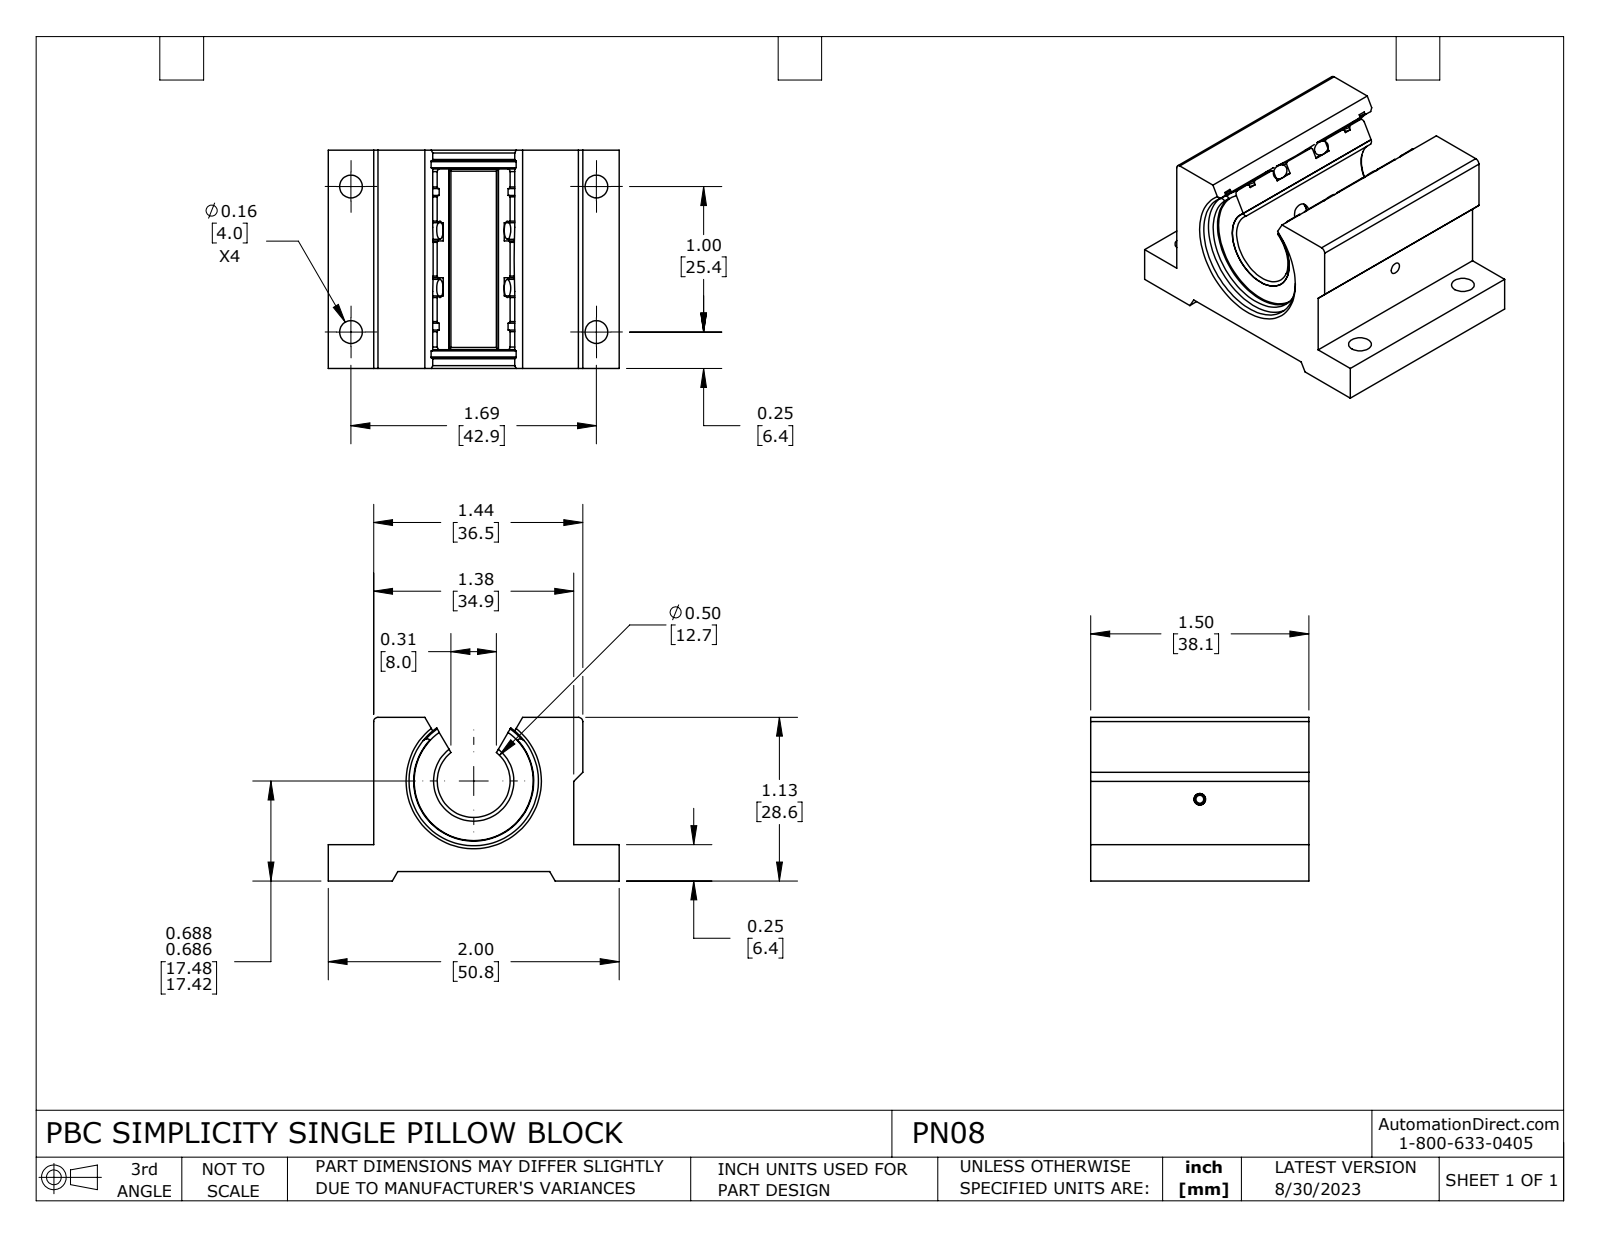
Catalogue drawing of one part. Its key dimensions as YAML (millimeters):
part_name: "PN08"
step_written_by: "SolidWorks 2021 (CONFIG_CONTROL_DESIGN)"
units: millimeters
bodies: {solids: 8, faces: 202, planar: 49, cylindrical: 94, other: 59}
overall_size: [50.8, 38.1, 28.6]
volume: 31120
surface_area: 17050
round_holes:
  - {diameter: 4, count: 4}
  - {diameter: 1.4, count: 1}
  - {diameter: 2, count: 1}
  - {diameter: 3.5, count: 1}
round_bosses_or_shafts:
  - {diameter: 22.2, count: 1}
  - {diameter: 20.8, count: 1}
  - {diameter: 18.1, count: 1}
  - {diameter: 2, count: 1}
partial_cylinders:
  - {radius: 0.8, count: 4}
  - {radius: 3, count: 2}
  - {radius: 6.4, count: 1}
  - {radius: 7, count: 1}
  - {radius: 10.5, count: 1}
  - {radius: 11.3, count: 1}
  - {radius: 11.8, count: 1}
  - {radius: 12.1, count: 1}
face_to_face_distances: [1.7, 6.4, 26.9, 28.6, 38.1, 4.7, 22.2, 8, 42.8, 34.9]
hole_center_spacings: [25.4, 42.8, 49.8]
